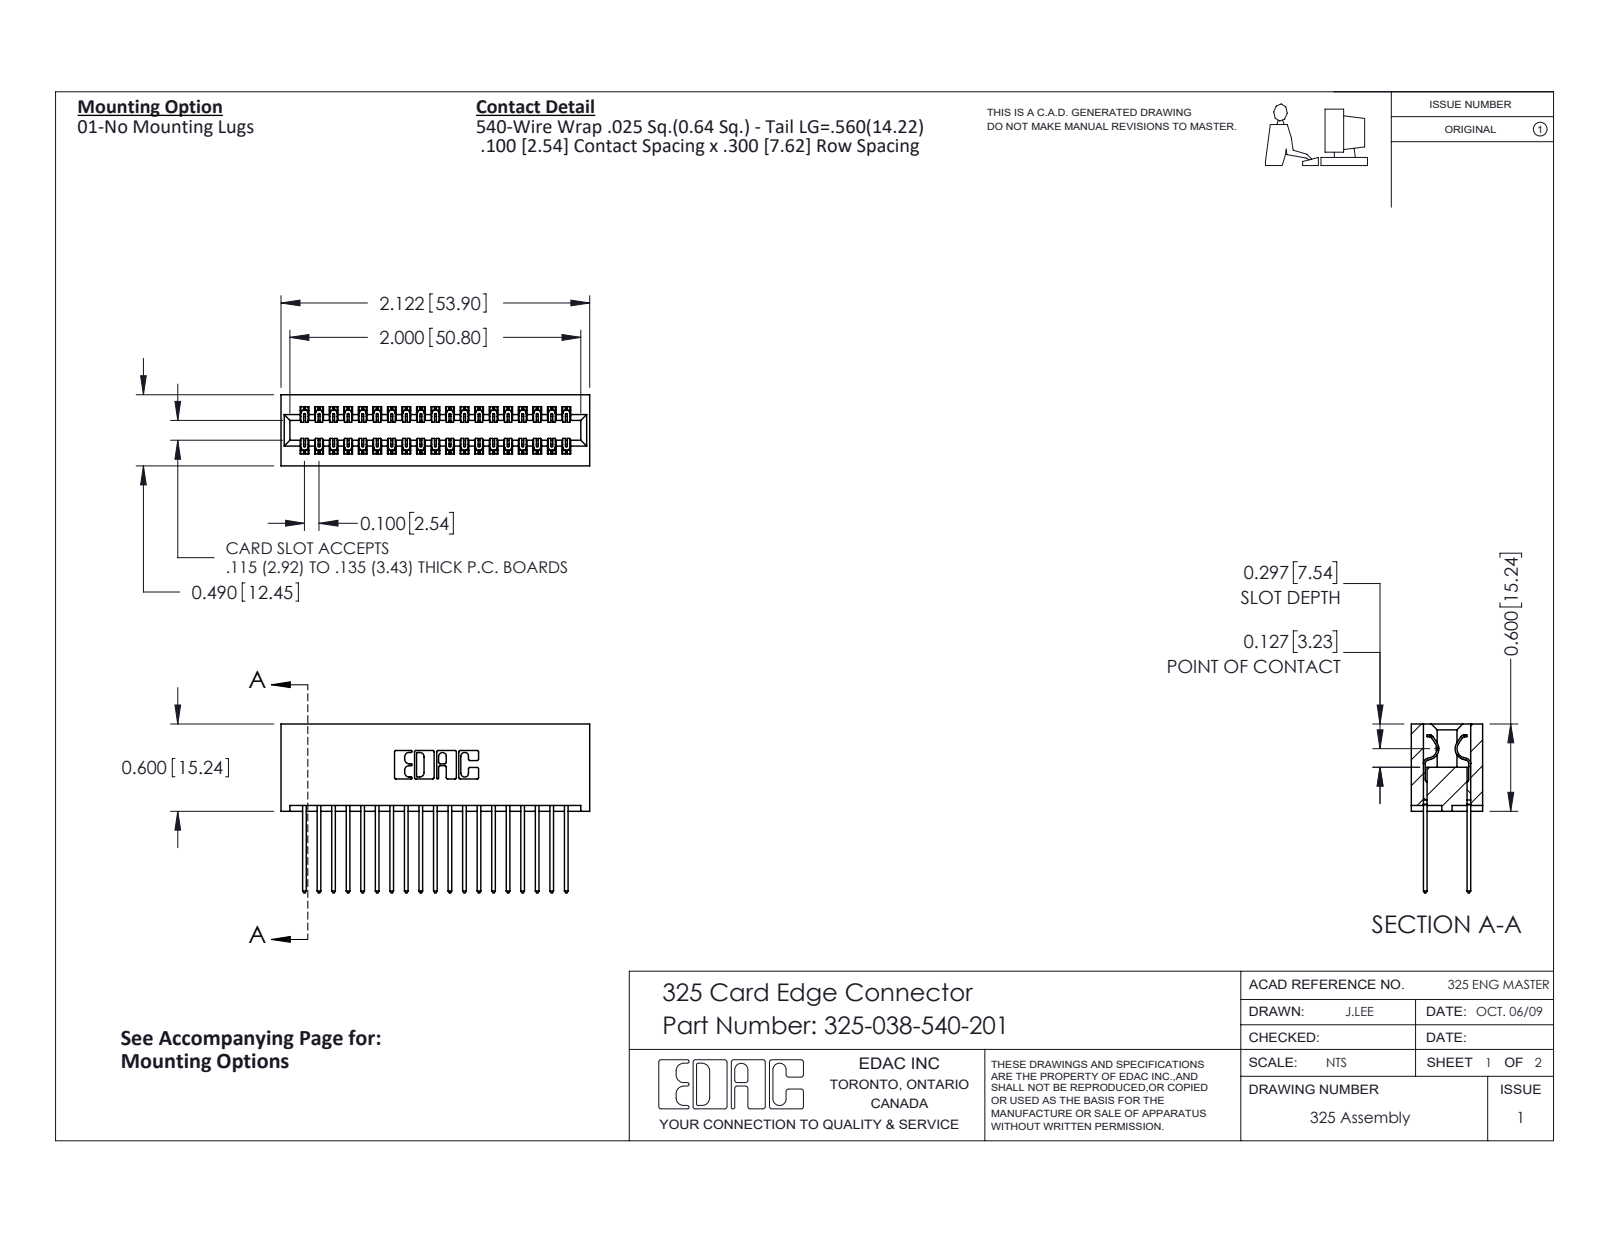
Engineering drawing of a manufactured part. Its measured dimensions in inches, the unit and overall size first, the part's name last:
Units: inches
Overall size (bounding box): 2.122 × 1.16 × 0.49
Partial cylindrical surfaces — rounded edges, fillets, slot ends (radius × count): R0.006 ×57, R0.01 ×38, R0.01 ×22, R0.007 ×6, R0.031 ×6, R0.026 ×3, R0.014 ×2, R0.022 ×2
Main face-to-face distances: 0.083, 0.407, 0.3, 0.107, 0.383, 0.025, 0.325, 0.49, 0.1, 0.275
Volume: 0.458 in³ · Surface area: 15.32 in²
Bodies: 39 solids, 2082 faces (1434 planar, 648 cylindrical, 0 other)
Part name (STEP PRODUCT): 325-038-540-201; 325-292-001_325-293-140; 325 Part_Lugless
STEP written by: SolidWorks 2016 (CONFIG_CONTROL_DESIGN)
